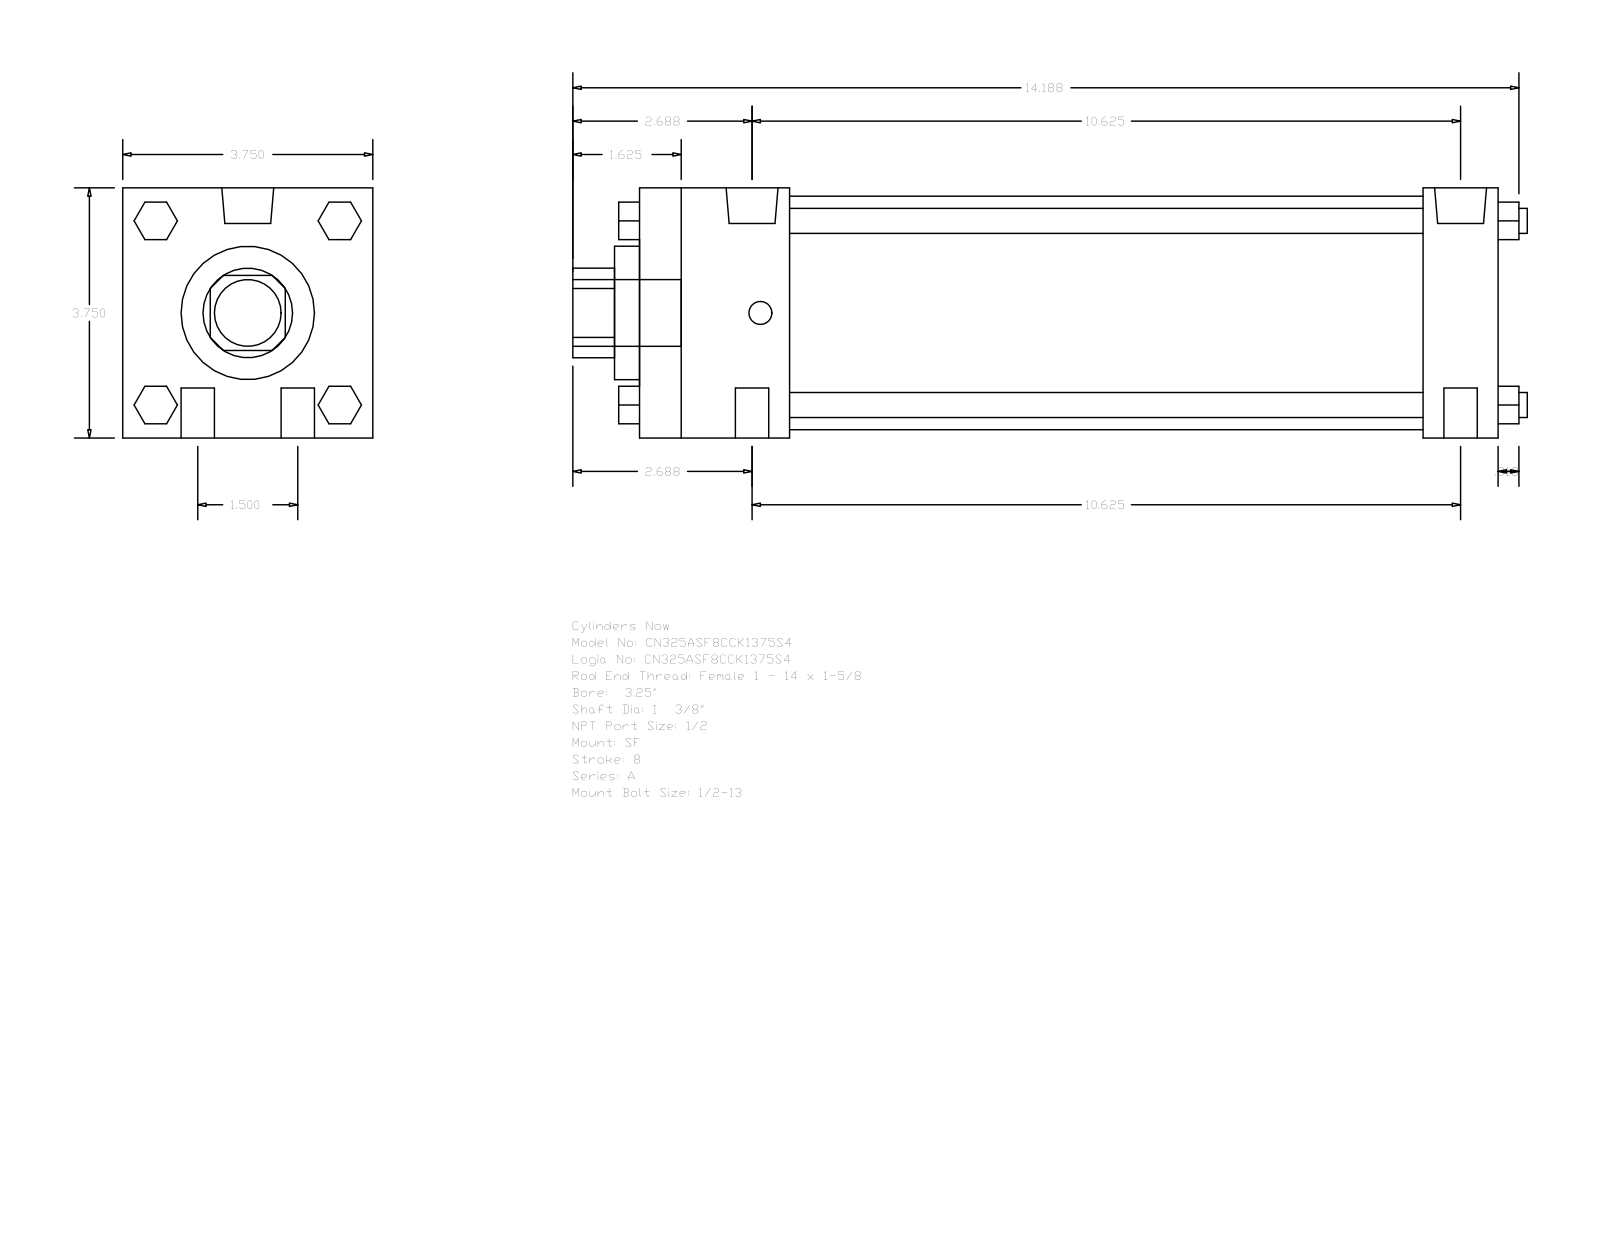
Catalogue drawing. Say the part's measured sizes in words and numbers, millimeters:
The part is named "A_SF__0325_1.375". Its 3-D file was written by "GSSL Pune (CONFIG_CONTROL_DESIGN)". It is 0 solids with 124 faces: 94 planar, 30 cylindrical and 0 other. Overall it measures 363.54 by 95.25 by 95.25 millimeters. Round holes: 1 of diameter 34.92, 1 of diameter 50.8, 1 of diameter 88.9. Round bosses or shafts: 4 of diameter 12.7, 4 of diameter 9.53, 2 of diameter 19.77, 2 of diameter 8.73, 1 of diameter 25.4. Partial cylindrical surfaces (rounded edges, fillets, slot ends): 1 of radius 17.06. The main face-to-face distances are 95.24, 327.03, 28.58, 298.45, 57.15, 241.3, 269.88, 9.52, 66.67, 307.97.
